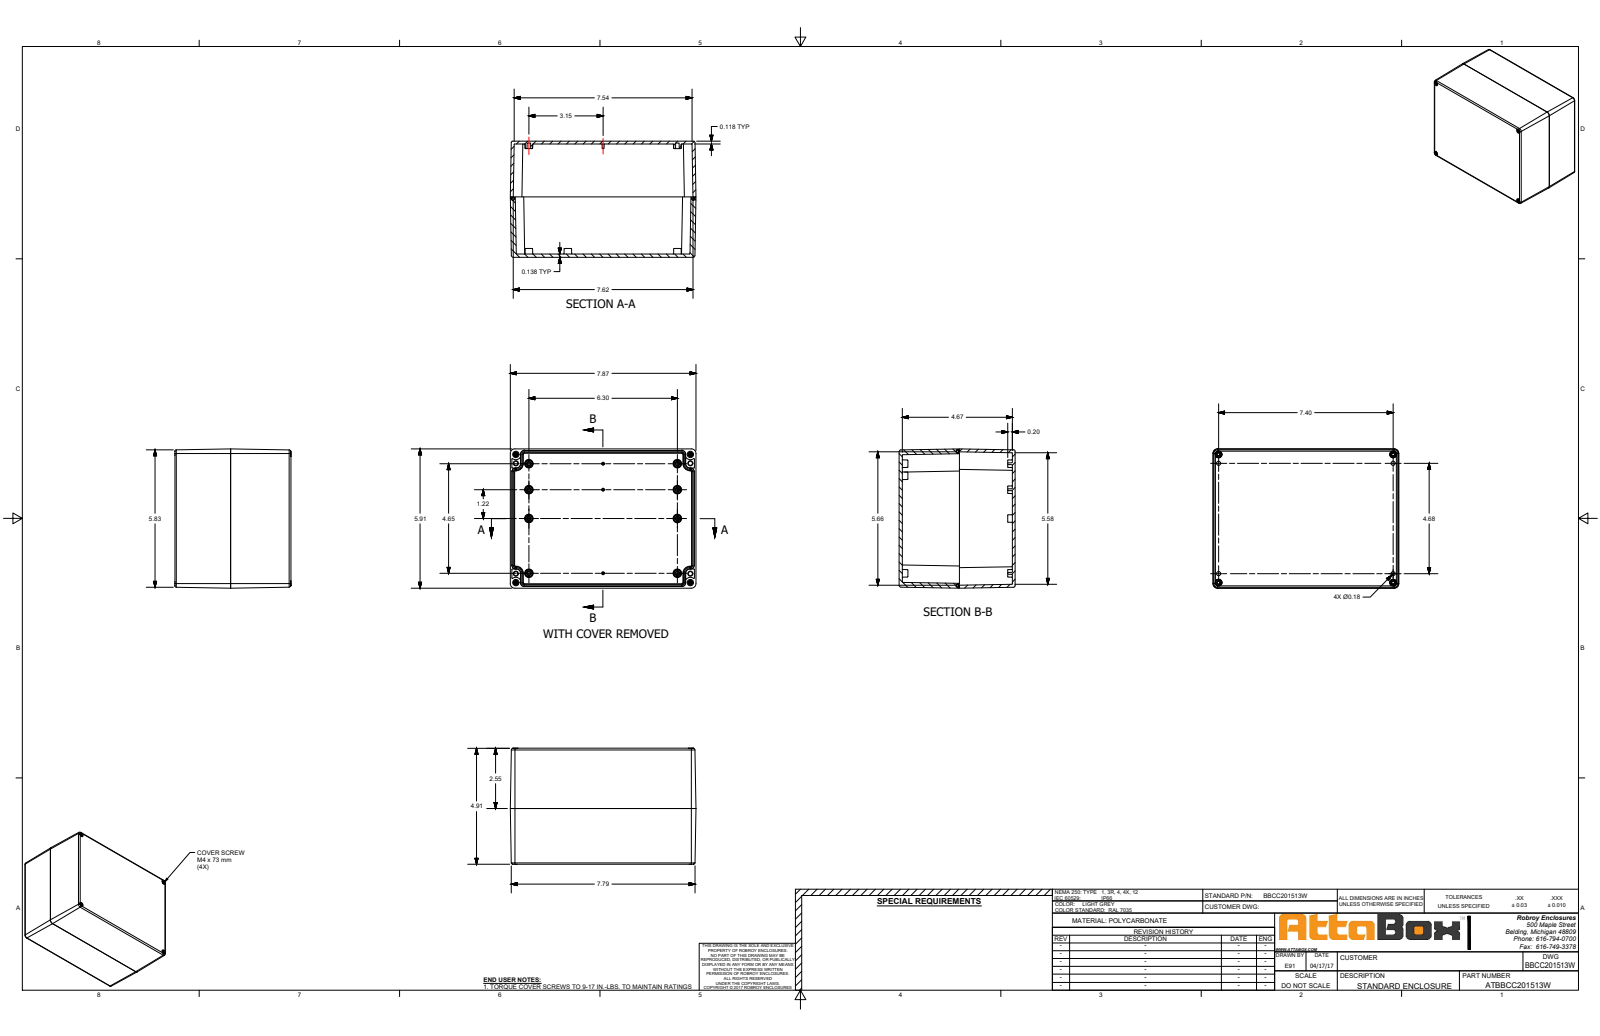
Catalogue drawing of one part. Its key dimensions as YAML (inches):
part_name: "BBCC201513W"
step_written_by: "SolidWorks 2018 (AUTOMOTIVE_DESIGN)"
units: inches
bodies: {solids: 11, faces: 1748, planar: 652, cylindrical: 428, other: 668}
overall_size: [7.874, 5.906, 4.921]
volume: 34.17
surface_area: 502.5
round_holes:
  - {diameter: 0.128, count: 4}
  - {diameter: 0.177, count: 4}
  - {diameter: 0.189, count: 4}
  - {diameter: 0.197, count: 4}
  - {diameter: 0.201, count: 4}
  - {diameter: 0.276, count: 4}
  - {diameter: 0.291, count: 4}
round_bosses_or_shafts:
  - {diameter: 0.268, count: 4}
  - {diameter: 0.173, count: 4}
  - {diameter: 0.157, count: 4}
  - {diameter: 0.13, count: 4}
partial_cylinders:
  - {radius: 0.055, count: 32}
  - {radius: 0.02, count: 28}
  - {radius: 0.039, count: 24}
  - {radius: 0.079, count: 12}
  - {radius: 0.201, count: 8}
  - {radius: 0.059, count: 4}
  - {radius: 0.094, count: 4}
  - {radius: 0.102, count: 4}
face_to_face_distances: [0.126, 4.921, 0.118, 4.803, 0.138, 4.783, 4.665, 5.906, 5.701, 0.205]
hole_center_spacings: [0.378, 5.055, 7.402, 7.411, 8.963, 4.677, 5.433, 8.756]
